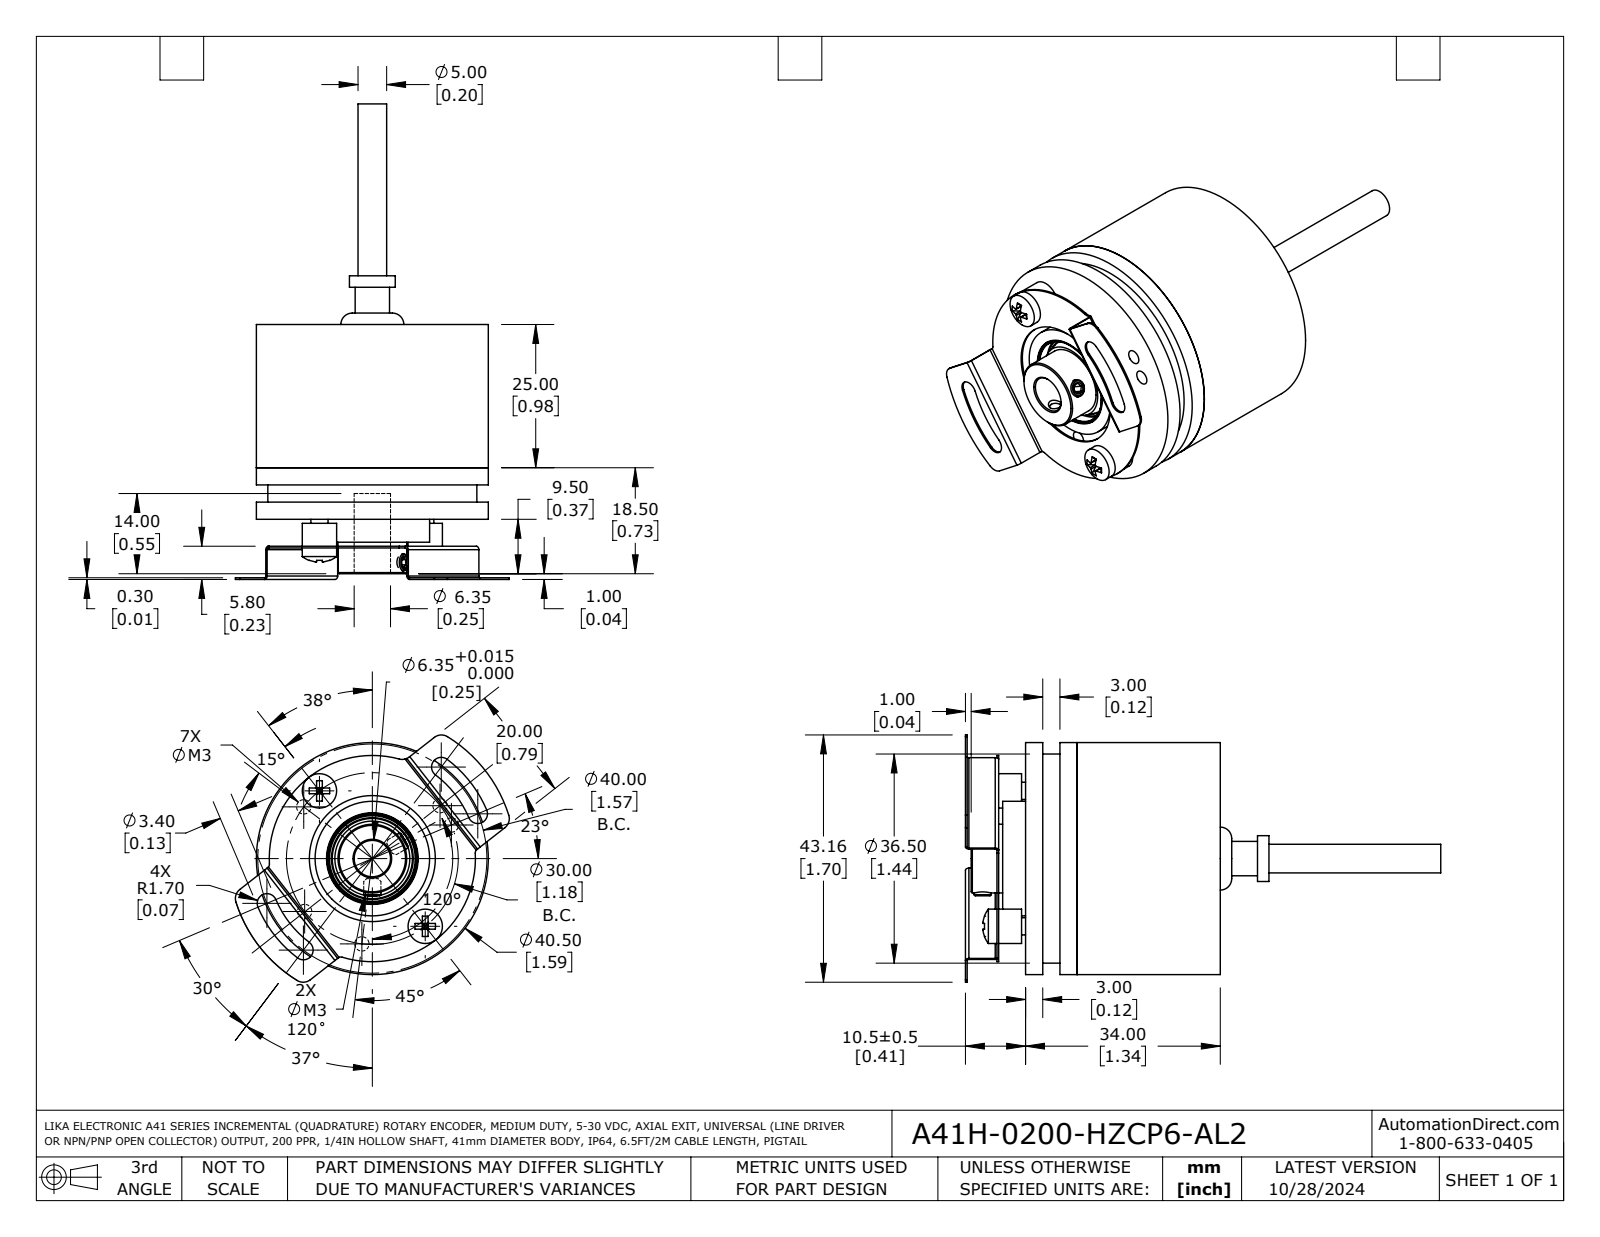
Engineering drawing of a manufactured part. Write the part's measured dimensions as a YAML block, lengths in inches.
part_name: "A41H-0200-HZCP6-AL2"
step_written_by: "SolidWorks 2021 (AUTOMOTIVE_DESIGN)"
units: inches
bodies: {solids: 15, faces: 465, planar: 139, cylindrical: 186, other: 140}
overall_size: [3.268, 1.883, 1.699]
volume: 1.187
surface_area: 32.38
round_holes:
  - {diameter: 0.098, count: 9}
  - {diameter: 0.063, count: 7}
  - {diameter: 0.157, count: 3}
  - {diameter: 0.087, count: 2}
  - {diameter: 0.126, count: 2}
  - {diameter: 0.138, count: 2}
  - {diameter: 0.169, count: 1}
  - {diameter: 0.25, count: 1}
  - {diameter: 0.295, count: 1}
  - {diameter: 0.512, count: 1}
  - {diameter: 0.602, count: 1}
  - {diameter: 0.612, count: 1}
round_bosses_or_shafts:
  - {diameter: 0.118, count: 4}
  - {diameter: 0.236, count: 3}
  - {diameter: 0.15, count: 2}
  - {diameter: 0.079, count: 2}
  - {diameter: 1.594, count: 1}
  - {diameter: 1.496, count: 1}
  - {diameter: 1.457, count: 1}
  - {diameter: 1.437, count: 1}
partial_cylinders:
  - {radius: 0.039, count: 14}
  - {radius: 0.008, count: 8}
  - {radius: 0.079, count: 5}
  - {radius: 0.012, count: 4}
  - {radius: 0.024, count: 4}
  - {radius: 0.067, count: 4}
  - {radius: 0.03, count: 3}
  - {radius: 0.709, count: 1}
face_to_face_distances: [0.118, 0.433, 1.339, 0.906, 0.197, 1.22, 0.079, 0.866, 0.039, 0.787]
hole_center_spacings: [0.591, 0.669, 0.835, 0.11, 0.118, 0.837, 0.945, 1.023]
